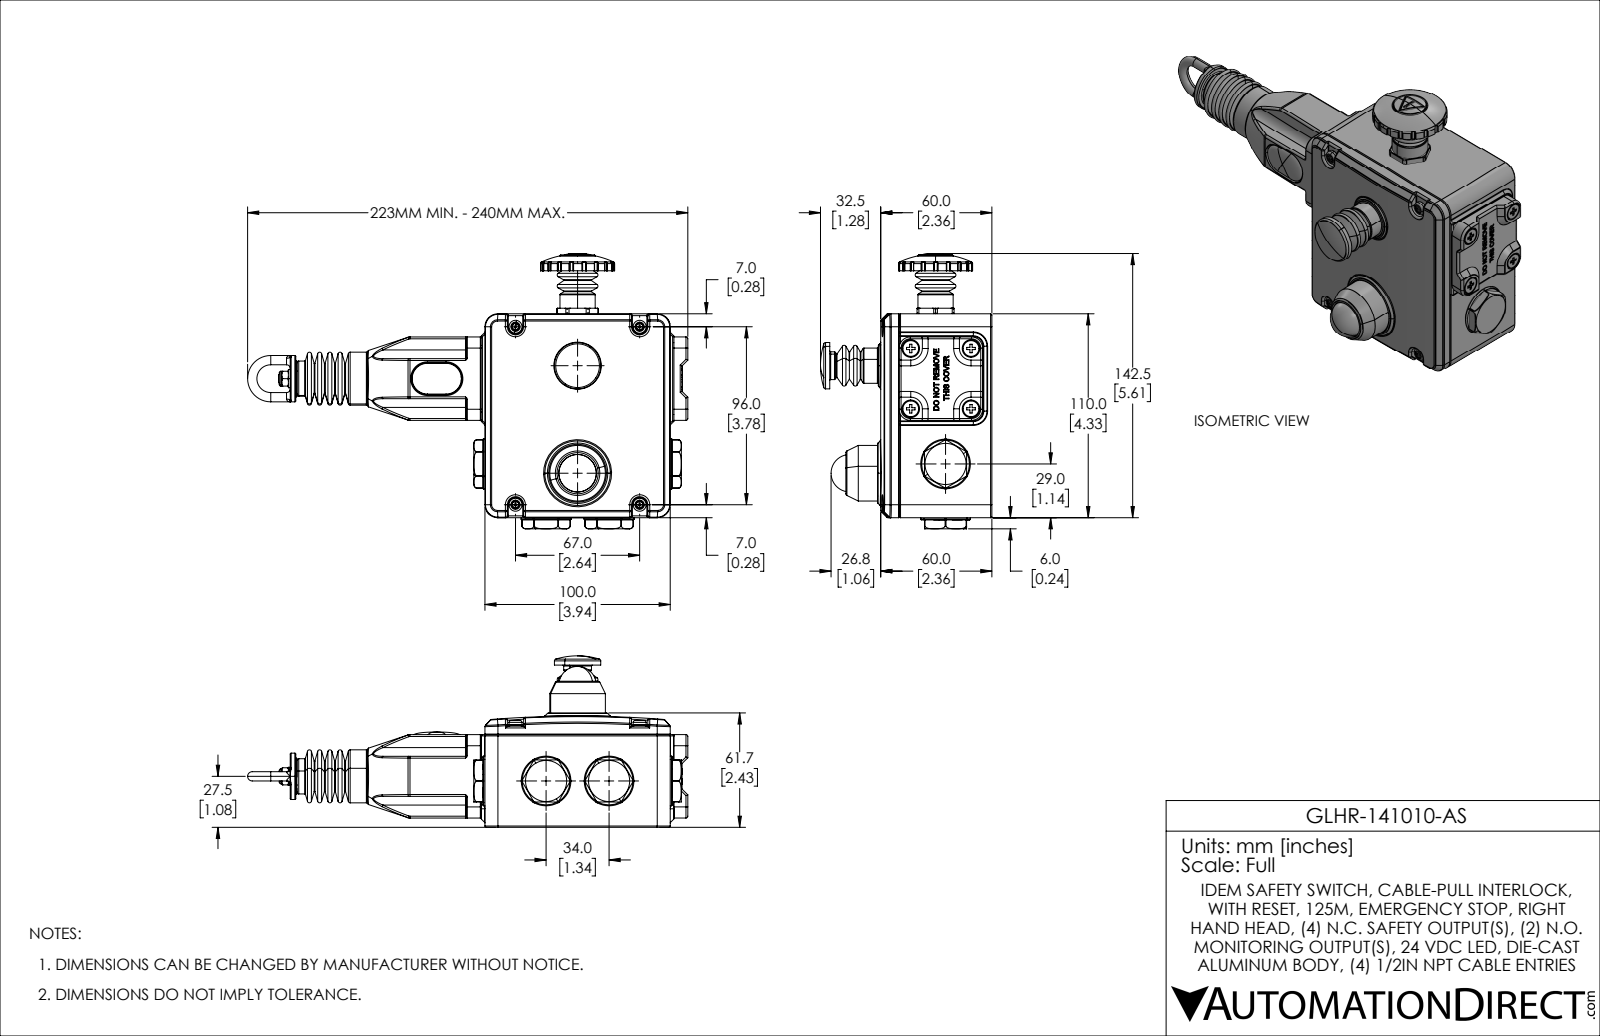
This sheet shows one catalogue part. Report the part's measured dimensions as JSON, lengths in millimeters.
{"part_name": "GLHR-141010-AS", "step_written_by": "SolidWorks 2021 (AUTOMOTIVE_DESIGN)", "units": "millimeters", "bodies": {"solids": 43, "faces": 4888, "planar": 1503, "cylindrical": 1638, "other": 1747}, "overall_size": [237.6, 148.5, 92.5], "volume_mm3": 307300, "surface_area_mm2": 193500, "round_holes": [[5, 11], [5.3, 9], [9.5, 7], [9, 6], [3.3, 4], [4, 4], [4.8, 4], [5.4, 4], [5.8, 4], [1.7, 3], [2.6, 3], [3, 3]], "round_bosses_or_shafts": [[8.5, 7], [6, 7], [4.4, 7], [5, 6], [7, 5], [3.5, 4], [1.3, 4], [26.8, 3]], "partial_cylinders_radius": [[0.5, 241], [1, 165], [0.2, 148], [0.7, 72], [0.3, 26], [0.2, 14], [0.1, 13], [6, 12]], "face_to_face_distances": [3.5, 54.8, 2.9, 51.9, 110, 1.4, 2, 4, 102, 98.5], "hole_center_spacings": [32.5, 32.5, 5.8, 9.5, 23, 48, 48.6, 76.5]}
